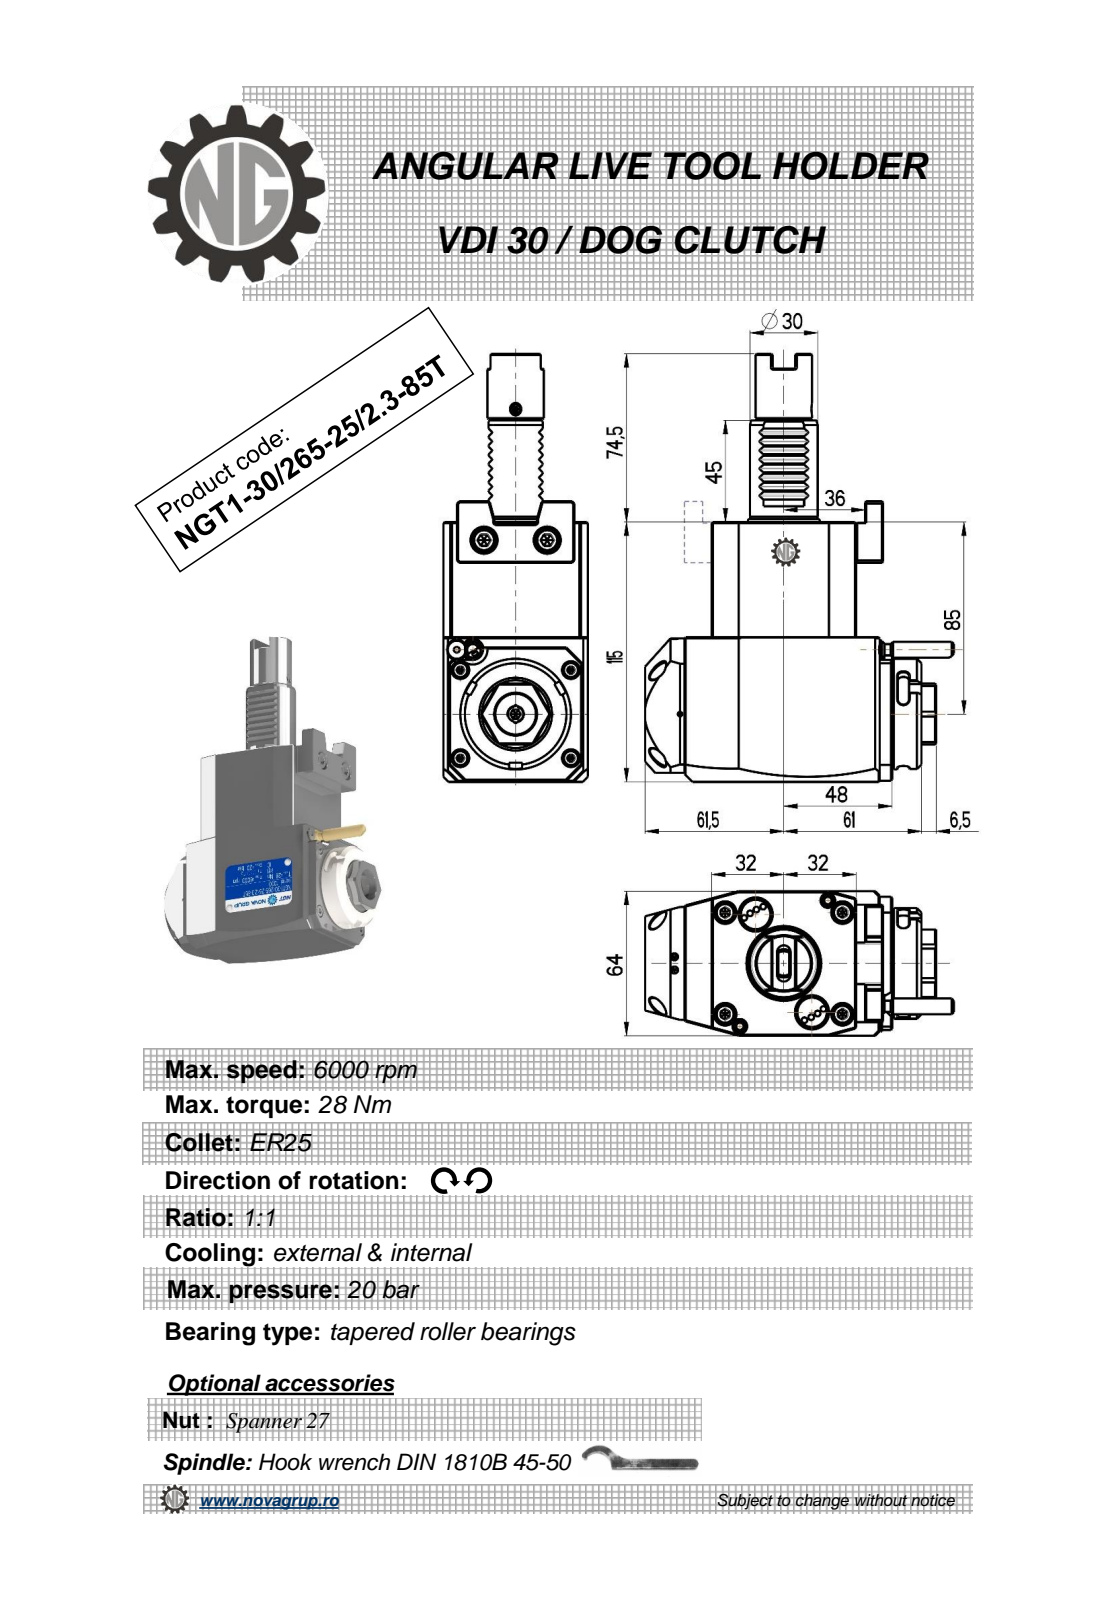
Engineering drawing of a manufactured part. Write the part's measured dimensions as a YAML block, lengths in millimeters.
part_name: "NGT1_30_265_25_1_3_85T"
step_written_by: "PRO/ENGINEER BY PARAMETRIC TECHNOLOGY CORPORATION, 2010280 (CONFIG_CONTROL_DESIGN)"
units: millimeters
bodies: {solids: 1, faces: 362, planar: 229, cylindrical: 71, other: 62}
overall_size: [189.5, 136.88, 64]
volume: 686226
surface_area: 59332
round_holes:
  - {diameter: 2.5, count: 1}
  - {diameter: 3, count: 1}
  - {diameter: 4.2, count: 1}
  - {diameter: 18, count: 1}
round_bosses_or_shafts:
  - {diameter: 49, count: 1}
  - {diameter: 42, count: 1}
  - {diameter: 30, count: 1}
  - {diameter: 25, count: 1}
  - {diameter: 20.85, count: 1}
  - {diameter: 8, count: 1}
  - {diameter: 7, count: 1}
  - {diameter: 5, count: 1}
partial_cylinders:
  - {radius: 0.3, count: 16}
  - {radius: 0.26, count: 6}
  - {radius: 2.5, count: 6}
  - {radius: 0.5, count: 2}
  - {radius: 1, count: 2}
  - {radius: 180, count: 2}
  - {radius: 4.5, count: 1}
  - {radius: 15, count: 1}
face_to_face_distances: [64, 115, 80, 16, 4, 12, 93, 29.5, 51, 17]
hole_center_spacings: [34.25, 108.18, 135]
